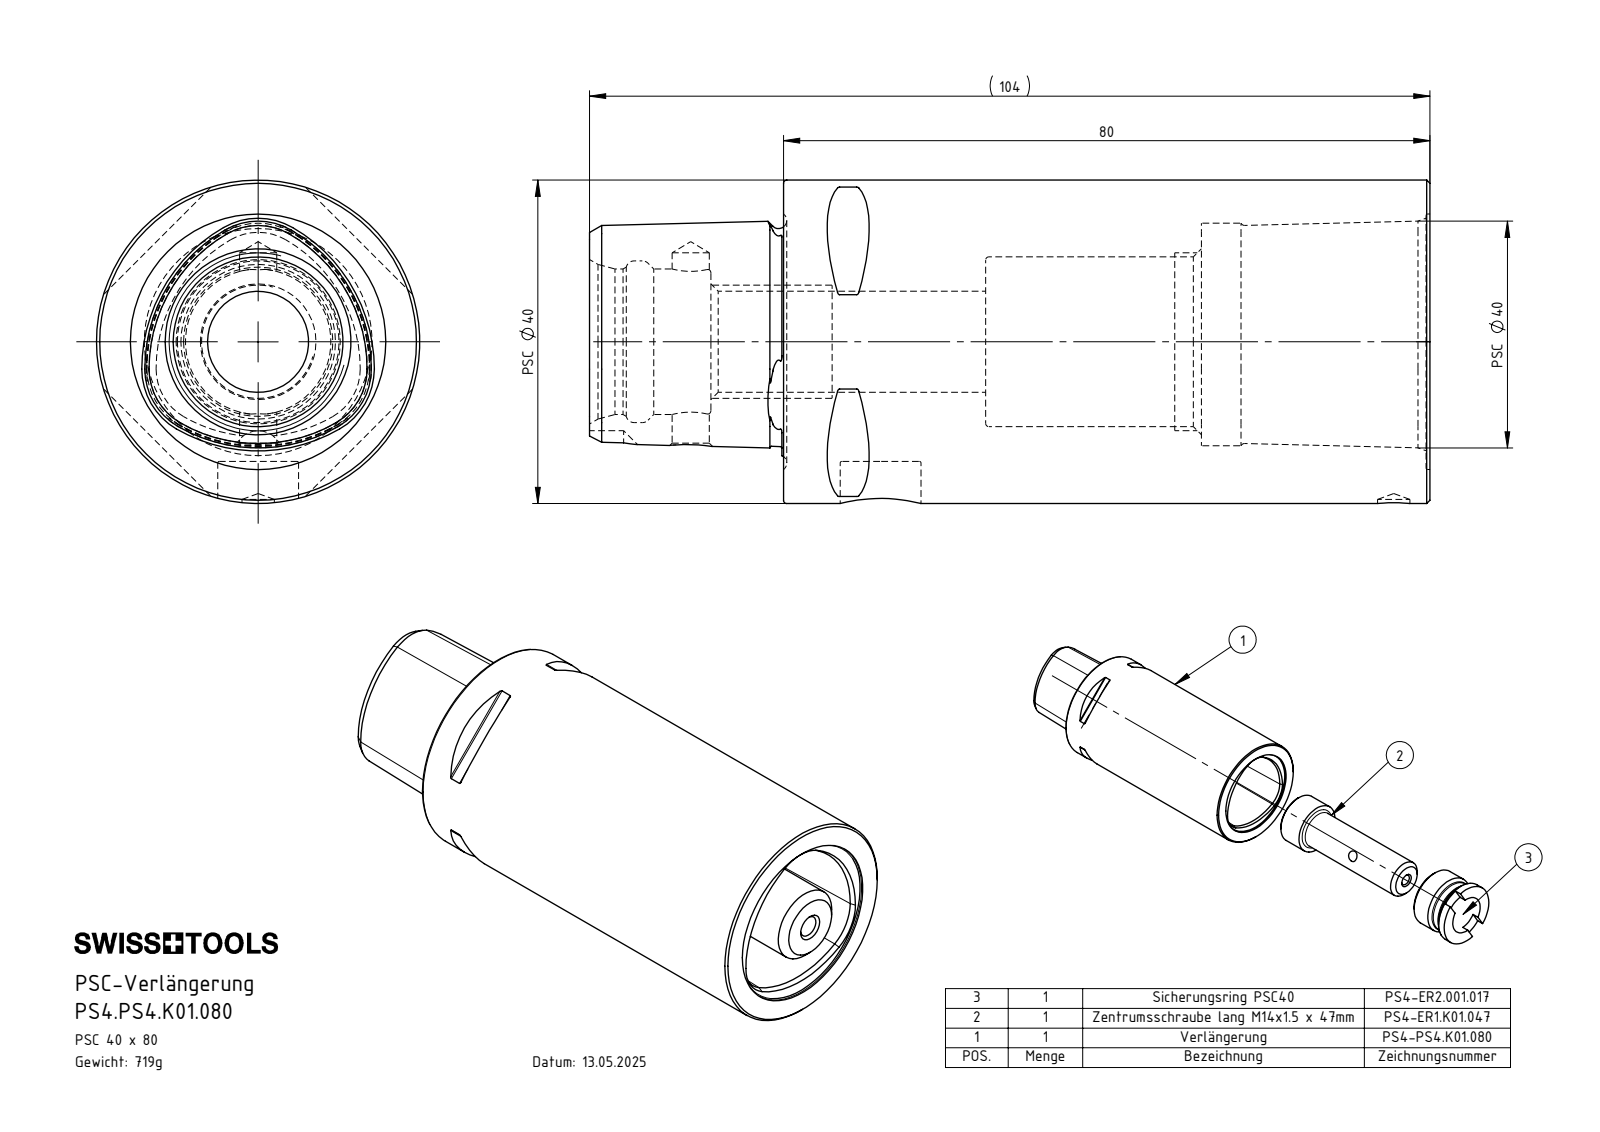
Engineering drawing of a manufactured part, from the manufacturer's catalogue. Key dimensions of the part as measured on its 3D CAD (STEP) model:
Part name (STEP PRODUCT): PS4-PS4.K01.080_A; PS4-ER2.001.017_A; PS4-ER1.K01.047_A_PreviewCfg; PS4.PS4.K01.080
STEP written by: SolidWorks 2022 (AUTOMOTIVE_DESIGN)
Units: millimetres
Bodies: 3 solids, 237 faces (47 planar, 54 cylindrical, 136 other)
Overall size (bounding box): 106 × 40 × 40
Volume: 91 612 mm³ · Surface area: 27 348 mm²
Round holes (diameter × count): ⌀4 ×3, ⌀4.6 ×1, ⌀10 ×1, ⌀12.5 ×1, ⌀14.4 ×1, ⌀18 ×1, ⌀20 ×1, ⌀21 ×1, ⌀31.6 ×1
Round bosses / shafts (diameter × count): ⌀40 ×1, ⌀23.4 ×1, ⌀22 ×1, ⌀19.6 ×1, ⌀18.9 ×1, ⌀14 ×1
Partial cylindrical surfaces — rounded edges, fillets, slot ends (radius × count): R0.3 ×8, R7.95 ×3, R19.58 ×3, R3 ×1
Main face-to-face distances: 80, 55, 25, 54.9, 29.9, 25.1, 49, 51.7, 26.7, 3.2
Hole centre spacings: 23.5, 63.5, 87
